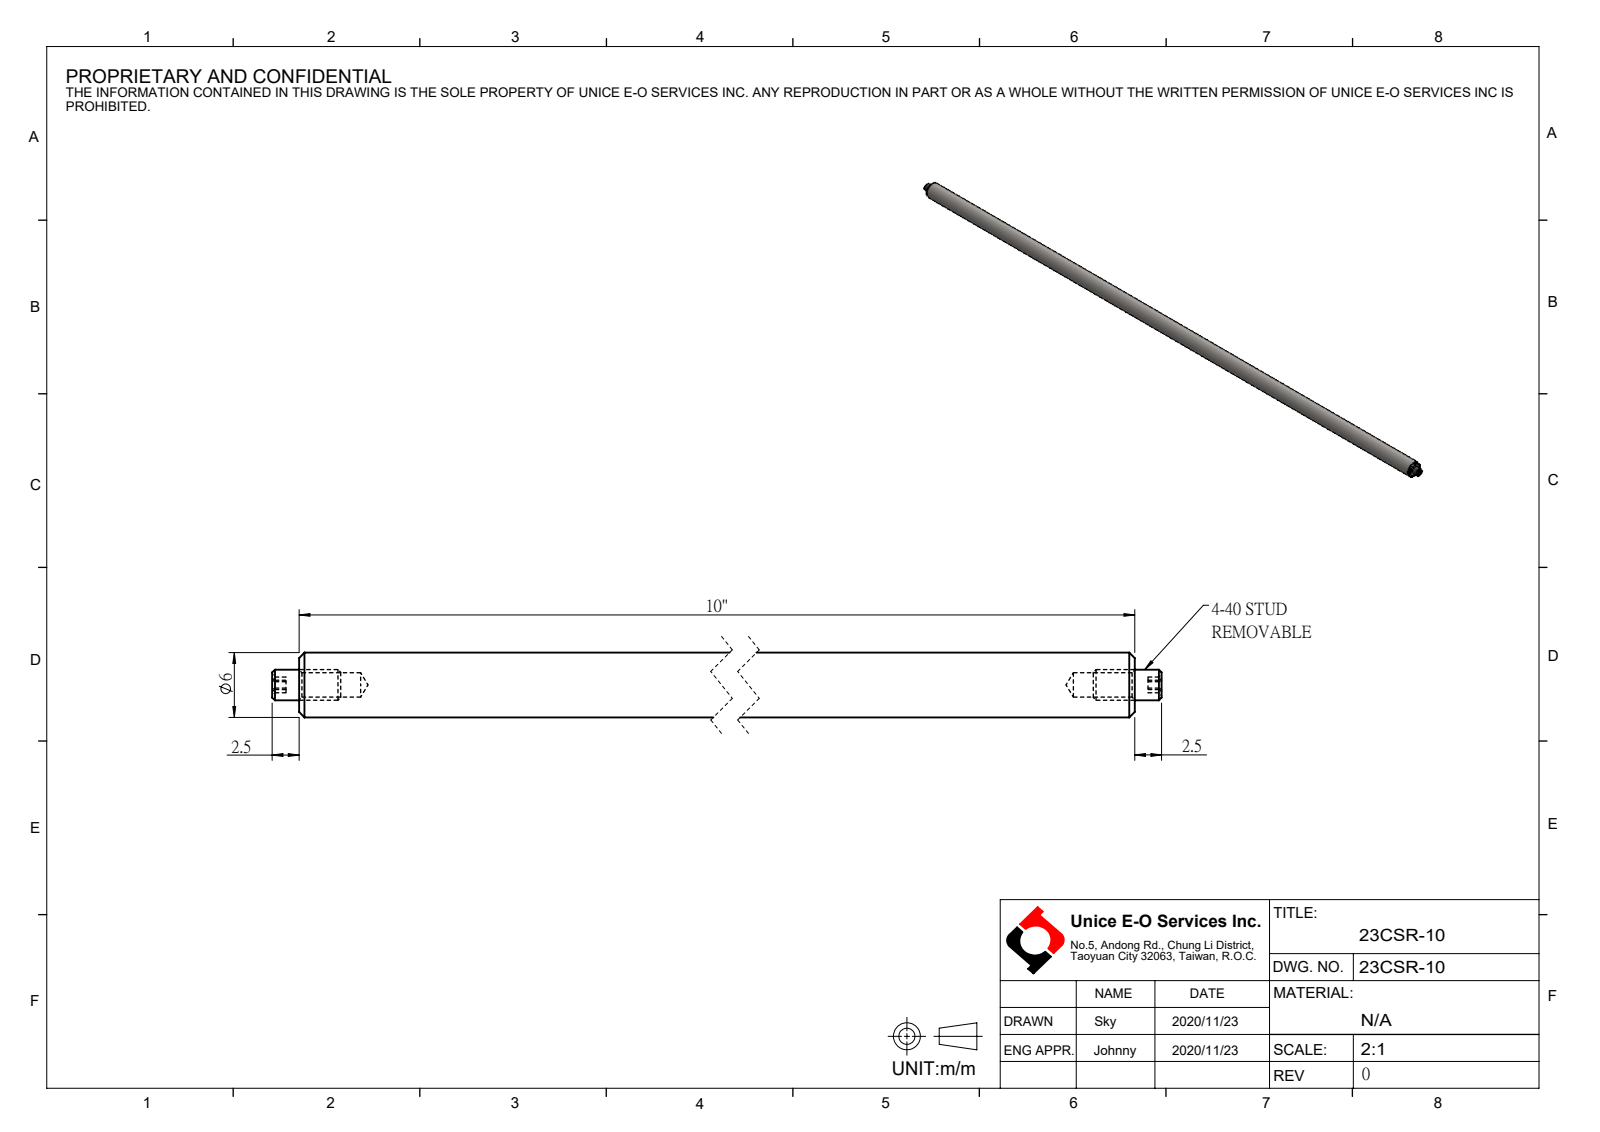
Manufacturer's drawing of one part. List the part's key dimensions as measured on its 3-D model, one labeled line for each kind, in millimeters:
Part name (STEP PRODUCT): 23CSR-10
STEP written by: SolidWorks 2016 (AUTOMOTIVE_DESIGN)
Units: millimetres
Bodies: 0 solids, 42 faces (28 planar, 6 cylindrical, 8 other)
Overall size (bounding box): 259 × 6 × 6
Round bosses / shafts (diameter × count): ⌀6 ×1, ⌀2.84 ×1
Main face-to-face distances: 254, 1.27, 2.5, 256.5, 259
